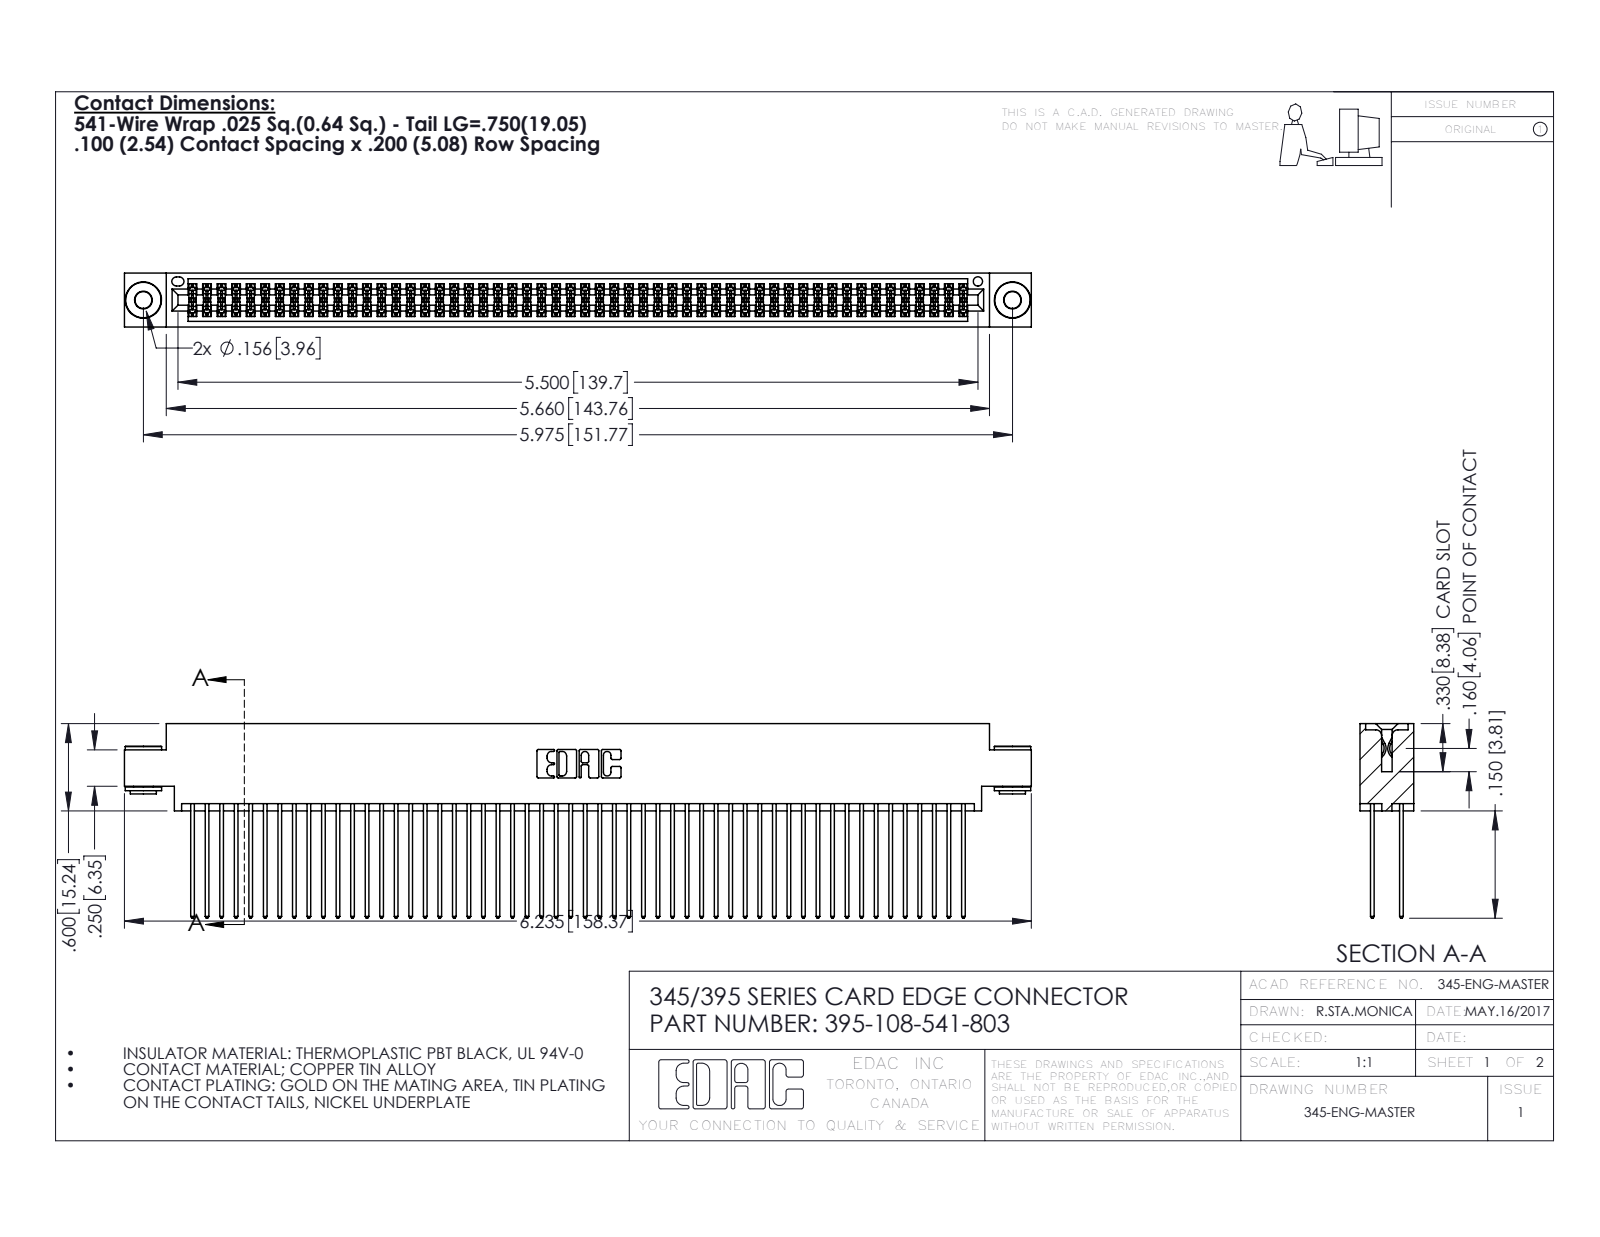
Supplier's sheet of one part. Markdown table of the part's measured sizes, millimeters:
| quantity | value |
| --- | --- |
| part name | 345 Part_0.170 Offset - 0.156 Dia-TH; 395-108-541-803; 345-292-001_345-293-141; 345-250-002_345-250-002-102 |
| STEP written by | SolidWorks 2016 (CONFIG_CONTROL_DESIGN) |
| units | millimeters |
| bodies | 111 solids, 5568 faces (3658 planar, 1902 cylindrical, 8 other) |
| overall size | 158.4 × 34 × 9.4 |
| volume | 16 000 mm³ |
| surface area | 27 170 mm² |
| round holes (diameter × count) | 2.9 × 2, 4 × 2, 1.6 × 1 |
| round bosses / shafts (diameter × count) | 6.4 × 2, 4.6 × 2, 3.5 × 2 |
| partial cylindrical surfaces (radius × count) | 0.2 × 162, 0.3 × 108, 0.3 × 22, 0.2 × 6, 0.8 × 6, 0.7 × 3, 0.4 × 2, 0.5 × 2 |
| main face-to-face distances | 1.8, 7.6, 5.1, 2.5, 6.9, 0.6, 9.4, 5.7, 4.4, 3.8 |
| hole center spacings | 6.9, 145.8, 151.8 |
